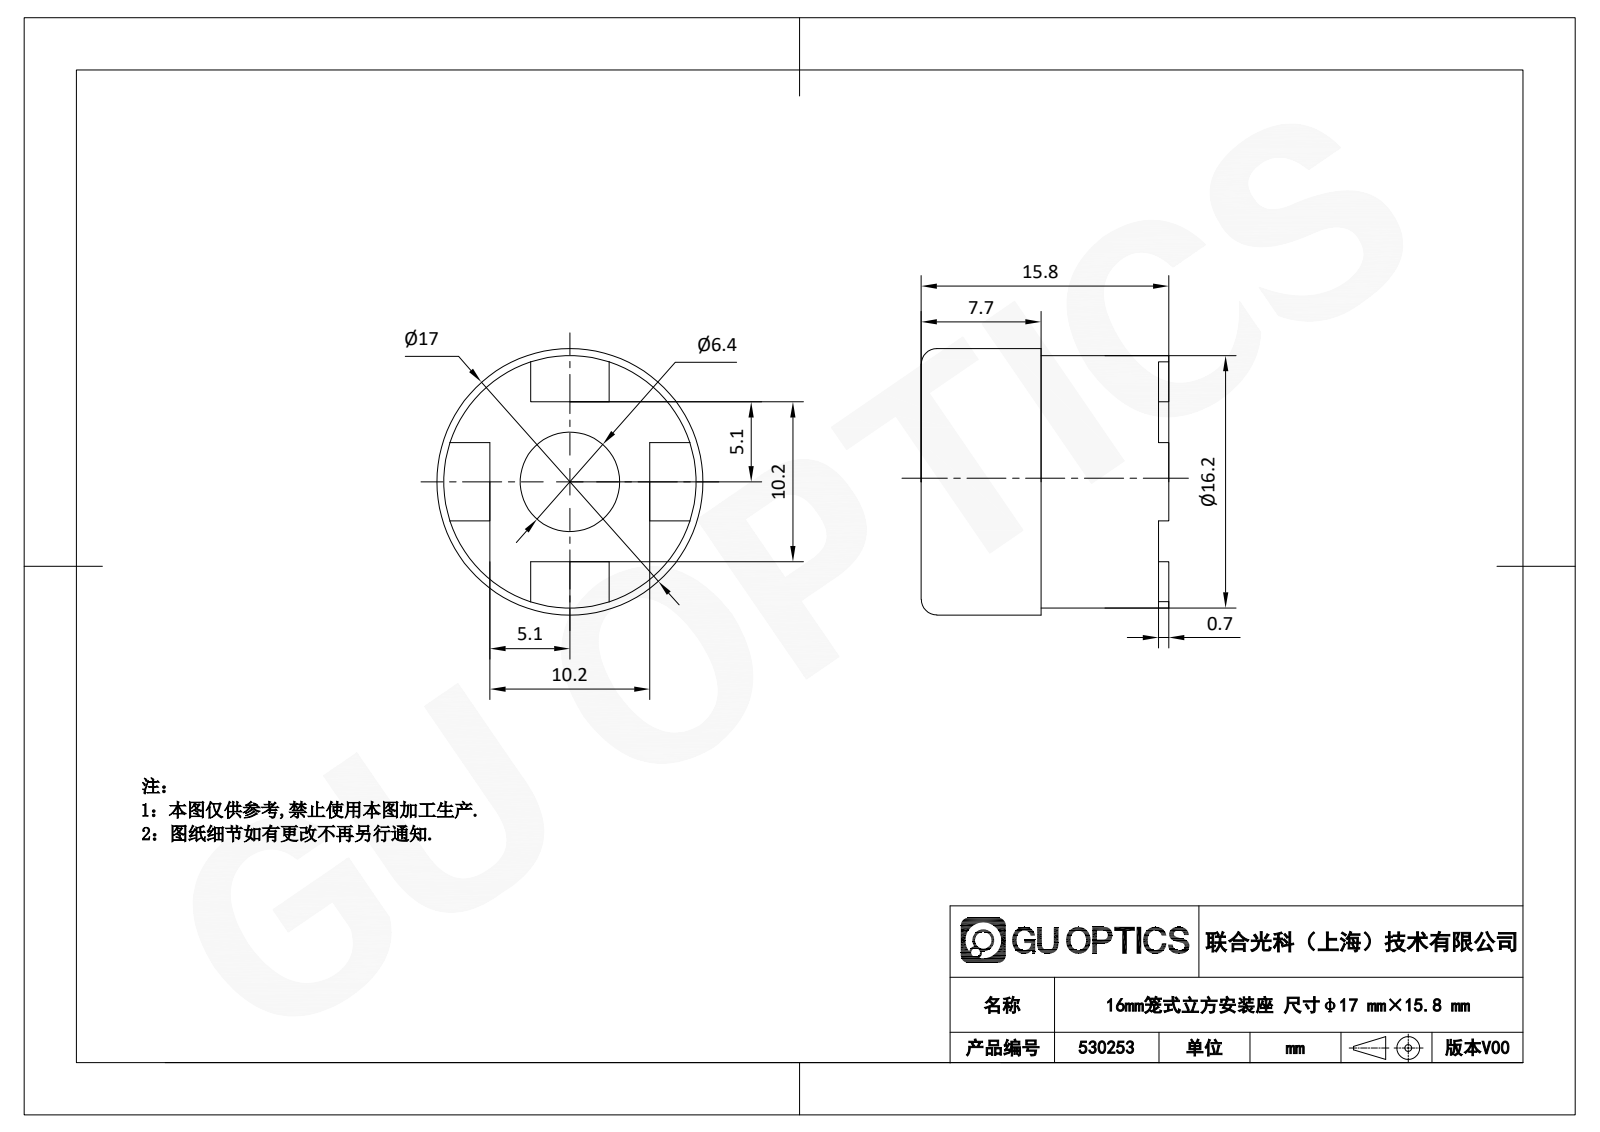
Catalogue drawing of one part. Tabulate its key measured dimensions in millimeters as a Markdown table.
| quantity | value |
| --- | --- |
| part name | 530253 |
| STEP written by | SolidWorks 2020 (CONFIG_CONTROL_DESIGN) |
| units | millimeters |
| bodies | 1 solid, 23 faces (19 planar, 3 cylindrical, 1 other) |
| overall size | 17 × 17 × 15.8 |
| volume | 2 808 mm³ |
| surface area | 1 497 mm² |
| round holes (diameter × count) | 6.35 × 1 |
| round bosses / shafts (diameter × count) | 17 × 1, 16.1 × 1 |
| main face-to-face distances | 15.15, 0.65, 15.8, 8.15, 7.5, 7.65, 2.6, 7.6, 5, 10.2 |
